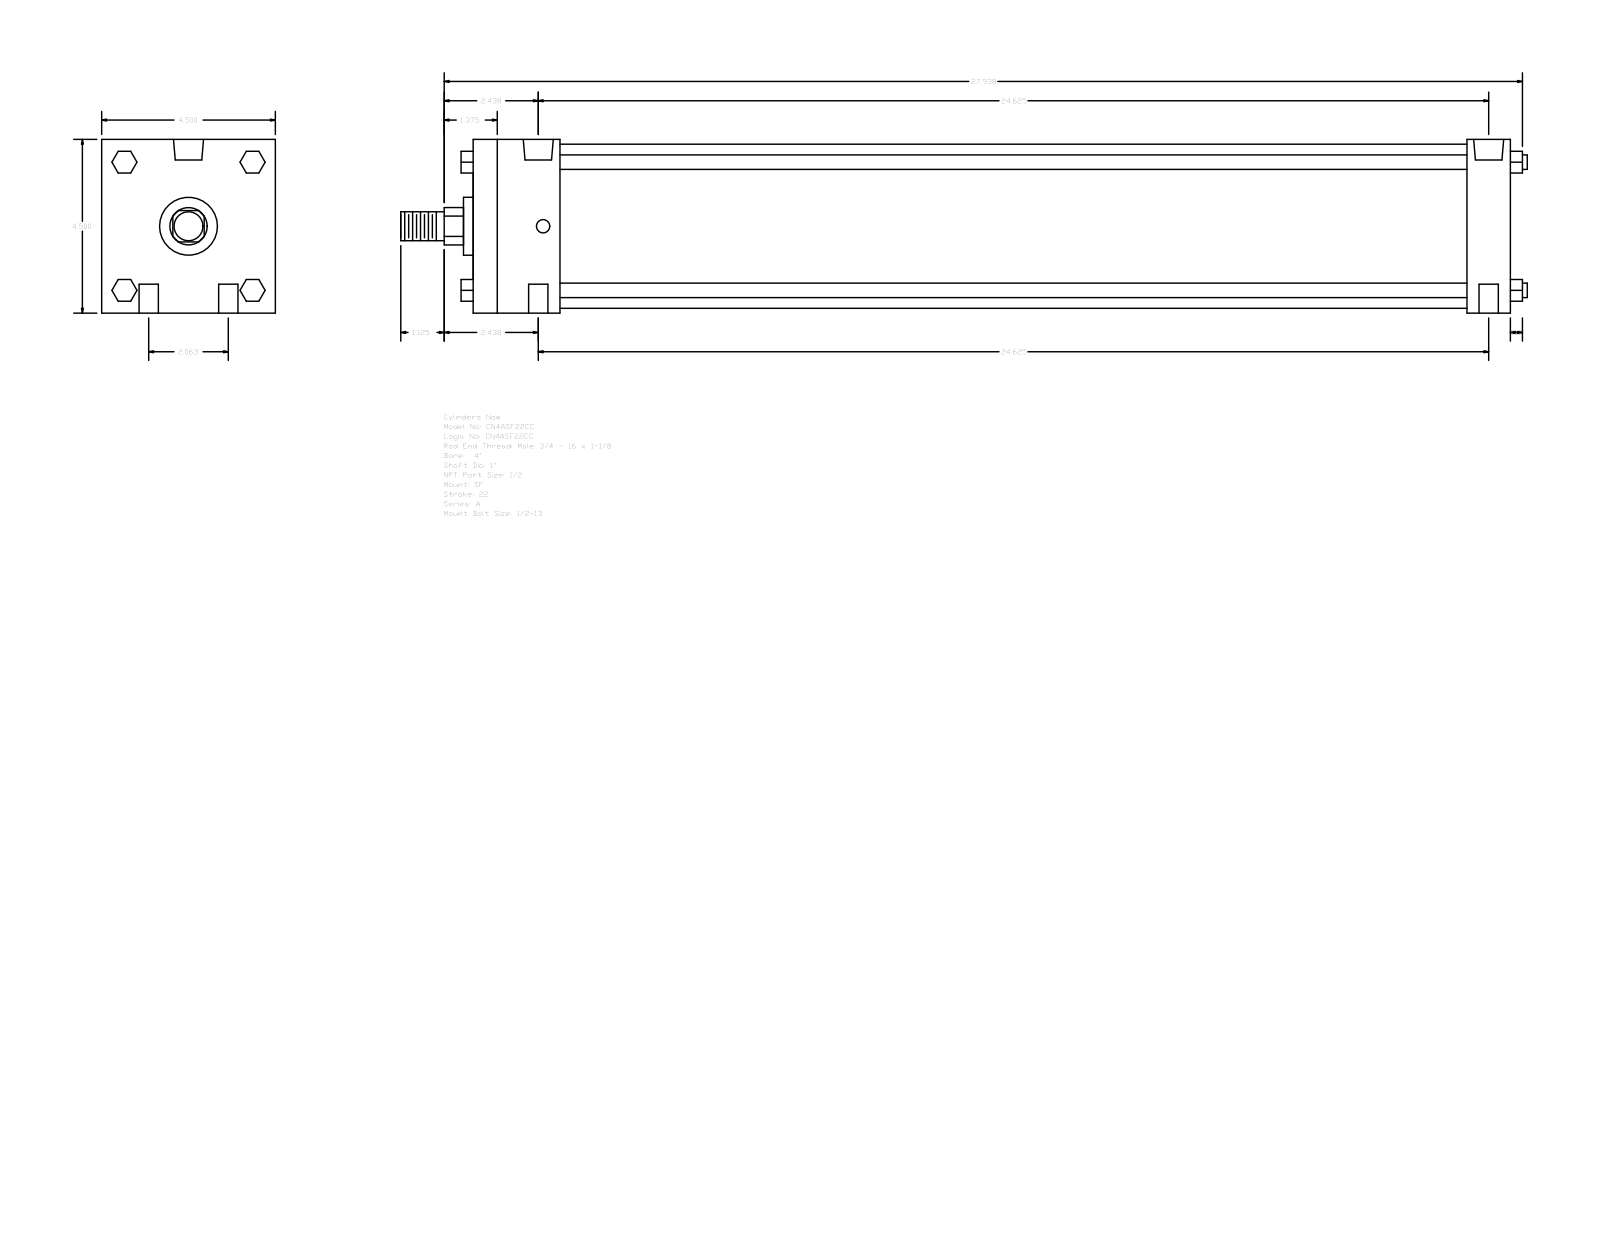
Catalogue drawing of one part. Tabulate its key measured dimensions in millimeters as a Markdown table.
| quantity | value |
| --- | --- |
| part name | A_SF__0400_1 |
| STEP written by | GSSL Pune (CONFIG_CONTROL_DESIGN) |
| units | millimeters |
| bodies | 0 solids, 124 faces (94 planar, 30 cylindrical, 0 other) |
| overall size | 741.36 × 114.3 × 114.3 |
| round holes (diameter × count) | 12.7 × 4, 8.73 × 2, 19.77 × 2 |
| round bosses / shafts (diameter × count) | 9.53 × 4, 107.95 × 1, 38.1 × 1, 25.4 × 1, 19.05 × 1 |
| partial cylindrical surfaces (radius × count) | 12.29 × 1 |
| main face-to-face distances | 114.3, 682.62, 28.57, 654.05, 57.15, 596.9, 625.47, 14.29, 42.16, 73.03 |
| hole center spacings | 26.19, 626.03, 625.48, 52.38, 627.67, 619.12 |
